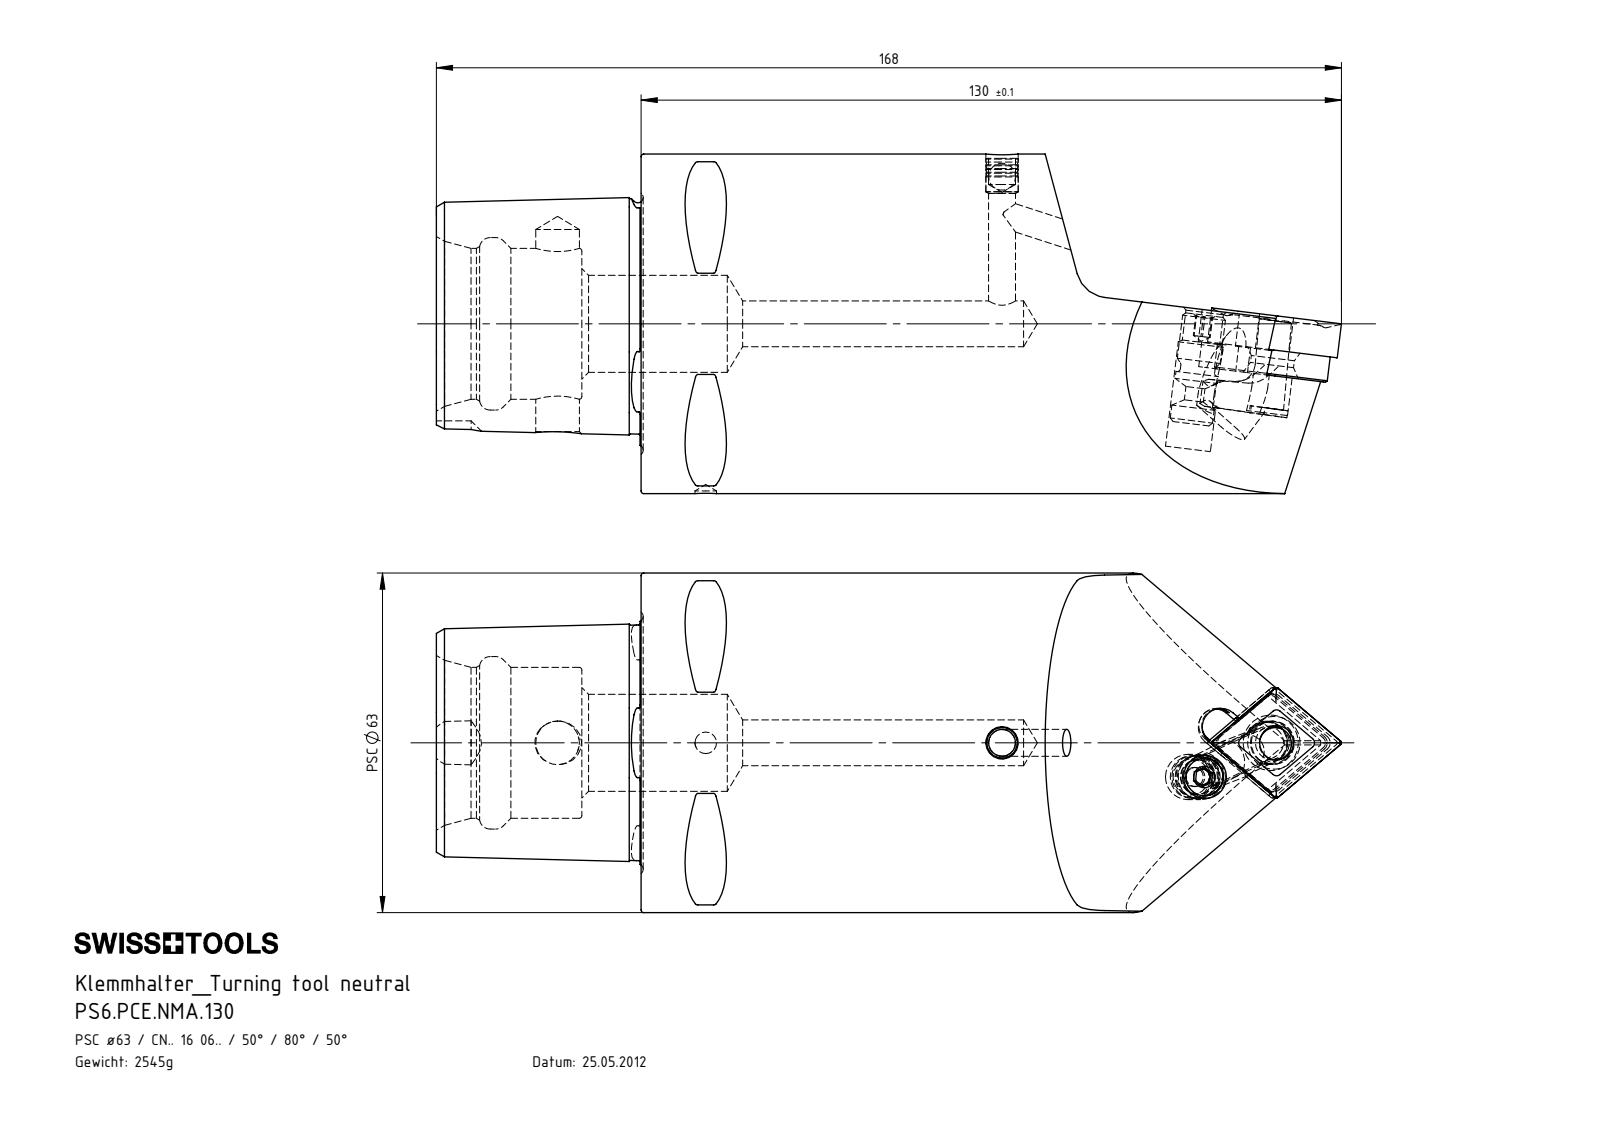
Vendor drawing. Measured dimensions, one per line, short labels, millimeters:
name: PS6-PCE.NMA.130; CNMG160604; WCE-ER2.101.004_A; WCE (+4 more)
written by: SolidWorks 2012 (CONFIG_CONTROL_DESIGN)
unit: mm
bodies: 7 solids, 323 faces (91 planar, 78 cylindrical, 154 other)
size: 168 × 63 × 63
volume: 323 034 mm³; area: 42 093 mm²
holes: 2× ⌀5, 1× ⌀4, 1× ⌀6.35, 1× ⌀7, 1× ⌀8.05, 1× ⌀8.1, 1× ⌀8.4, 1× ⌀8.5, 1× ⌀18, 1× ⌀28, 1× ⌀32
bosses: 2× ⌀6, 1× ⌀63, 1× ⌀8, 1× ⌀7.9, 1× ⌀6.4, 1× ⌀3.55
rounds: 8× R0.5, 4× R0.4, 4× R1.5, 3× R3.5, 2× R6, 1× R3.1, 1× R3.75, 1× R4
face distances: 38, 5.85, 24.88, 4.77, 10.62, 27, 11, 15.87, 0.8, 15.07
hole spacings: 14.76, 15.01, 27.5, 55, 82.5
